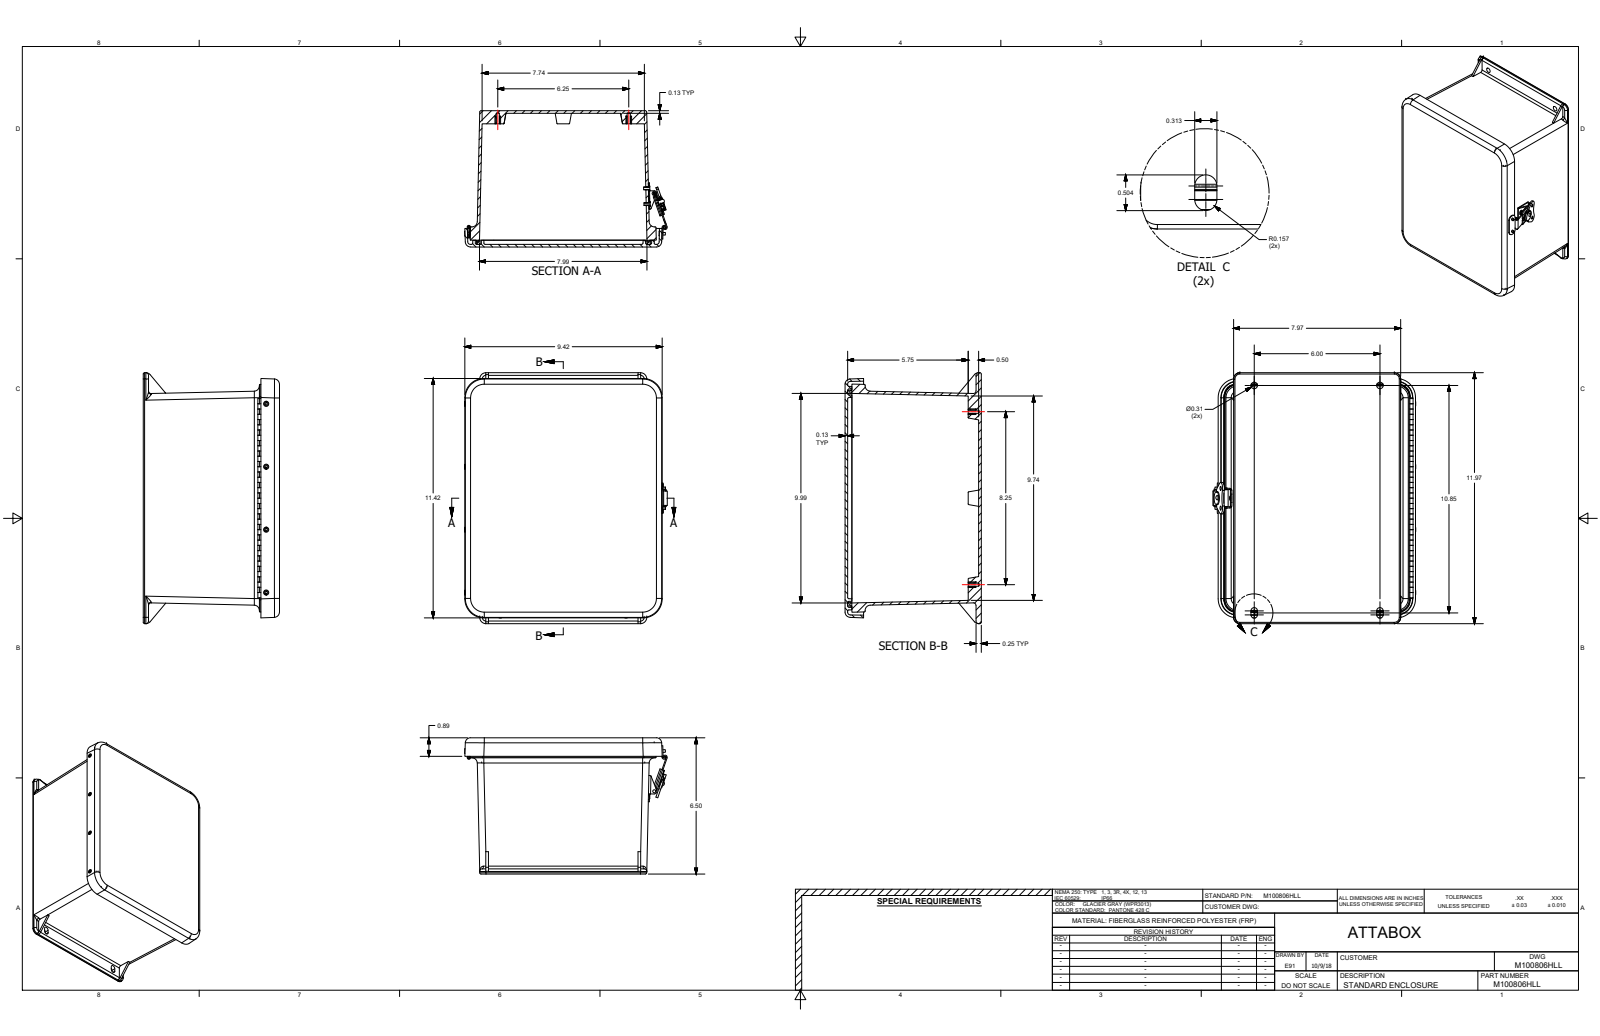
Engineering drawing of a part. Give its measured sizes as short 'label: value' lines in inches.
name: M100806HLL
written by: SolidWorks 2018 (AUTOMOTIVE_DESIGN)
unit: in
bodies: 40 solids, 1189 faces (467 planar, 461 cylindrical, 261 other)
size: 11.966 × 9.689 × 6.499
volume: 76.62 in³; area: 1 029 in²
holes: 13× ⌀0.14, 12× ⌀0.104, 12× ⌀0.152, 12× ⌀0.159, 8× ⌀0.131, 4× ⌀0.375, 2× ⌀0.13, 2× ⌀0.133, 2× ⌀0.187, 2× ⌀0.191, 2× ⌀0.313, 1× ⌀0.067
bosses: 12× ⌀0.27, 8× ⌀0.125, 5× ⌀0.125, 1× ⌀0.66, 1× ⌀0.582, 1× ⌀0.525, 1× ⌀0.286, 1× ⌀0.213
rounds: 26× R0.031, 20× R0.063, 19× R0.125, 18× R0.063, 16× R0.039, 16× R0.062, 12× R0.3, 11× R0.25
face distances: 0.125, 6.499, 0.123, 0.122, 6.374, 6.249, 0.125, 6.374, 6.172, 6.047
hole spacings: 6, 3, 2.5, 3.5, 8.5, 9, 0.937, 0.75
